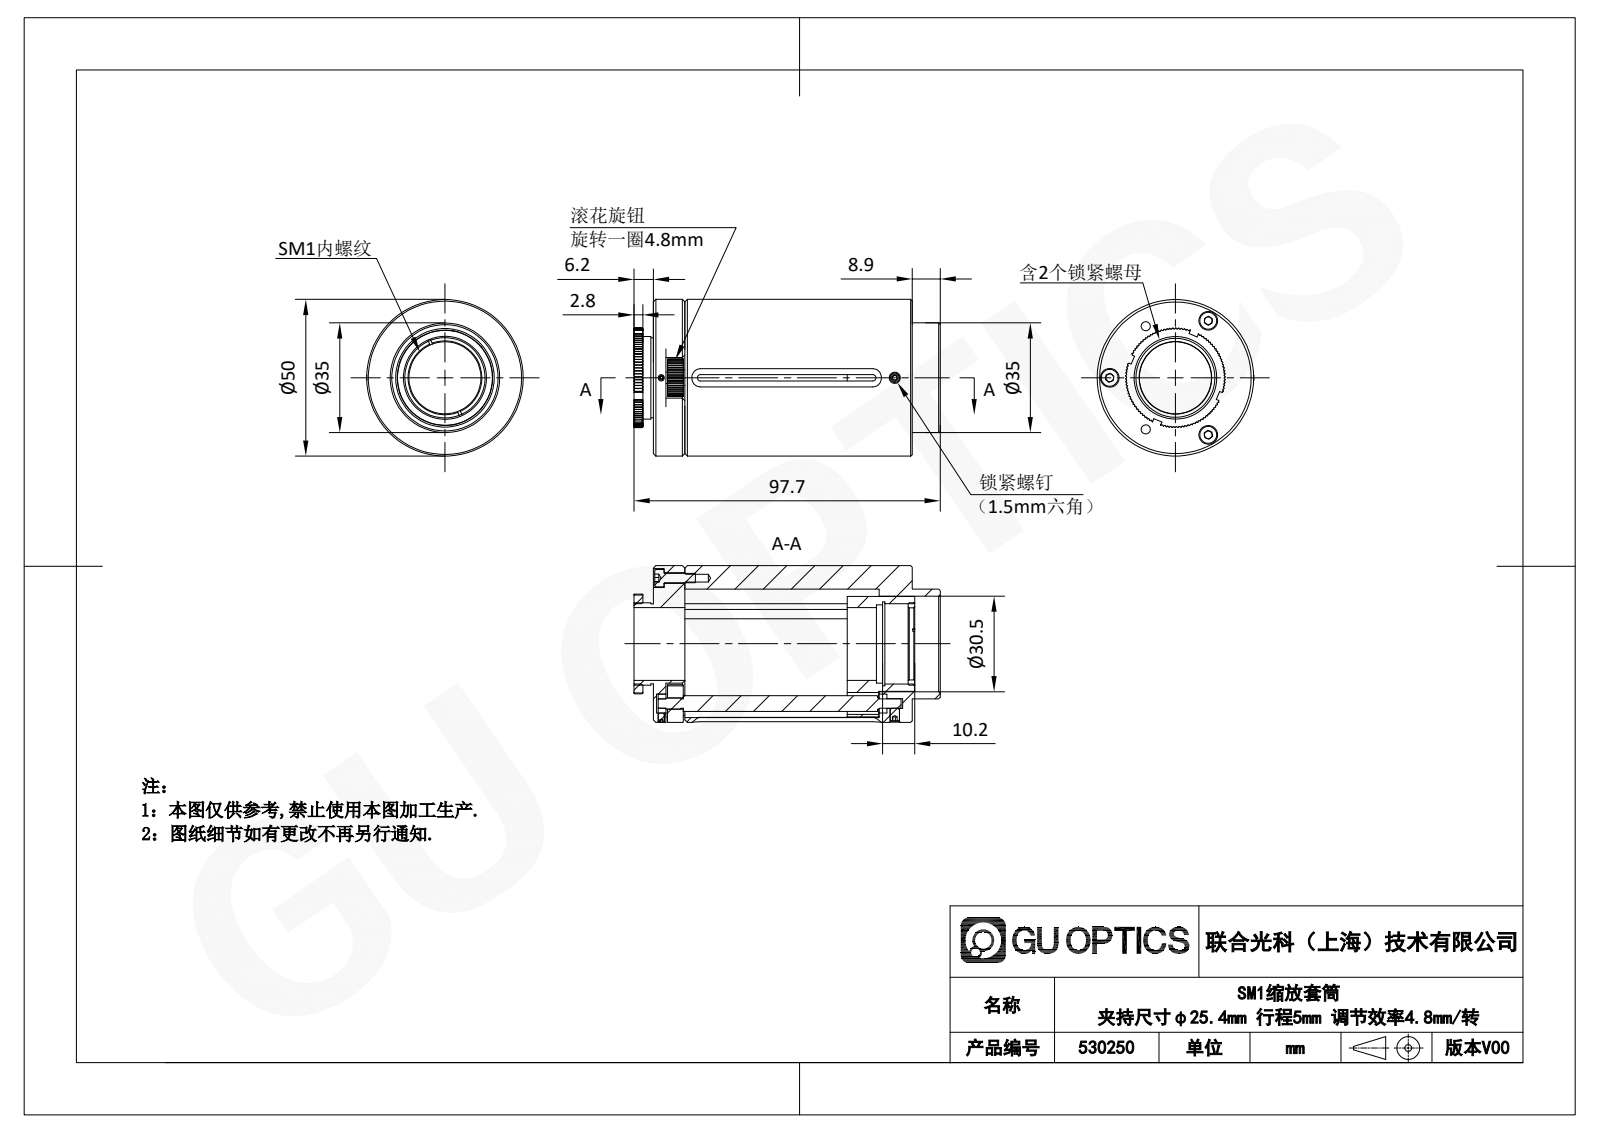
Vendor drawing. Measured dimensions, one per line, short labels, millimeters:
name: hex socket set screws with flat point gb_GB_FASTENER_SCREWS_HSFP M2X3-N; 530249; hexagon socket head cap screws gb_GB_FASTENER_SCREWS_HSHCS M3X10-N; hex socket set screws with flat point gb_GB_FASTENER_SCREWS_HSFP M3X4-N
written by: SolidWorks 2020 (CONFIG_CONTROL_DESIGN)
unit: mm
bodies: 19 solids, 1076 faces (490 planar, 331 cylindrical, 255 other)
size: 97.7 × 50 × 50
volume: 92 037 mm³; area: 43 150 mm²
holes: 7× ⌀3, 4× ⌀6, 3× ⌀2.5, 3× ⌀3.4, 3× ⌀7, 1× ⌀2, 1× ⌀3.1, 1× ⌀23, 1× ⌀23.2, 1× ⌀23.25, 1× ⌀25, 1× ⌀25.6
bosses: 4× ⌀3, 3× ⌀5.5, 1× ⌀50, 1× ⌀30.3, 1× ⌀26.3, 1× ⌀26.29, 1× ⌀25.5, 1× ⌀5
rounds: 96× R0.25, 14× R2, 3× R4.25, 3× R4.5, 2× R1, 1× R6, 1× R6.5, 1× R15.9
face distances: 10, 82.6, 72.6, 61.85, 51.85, 20.75, 10.15, 72, 62, 10.6
hole spacings: 20.08, 19, 21, 40, 20.07, 32.91, 36.37, 71.1
